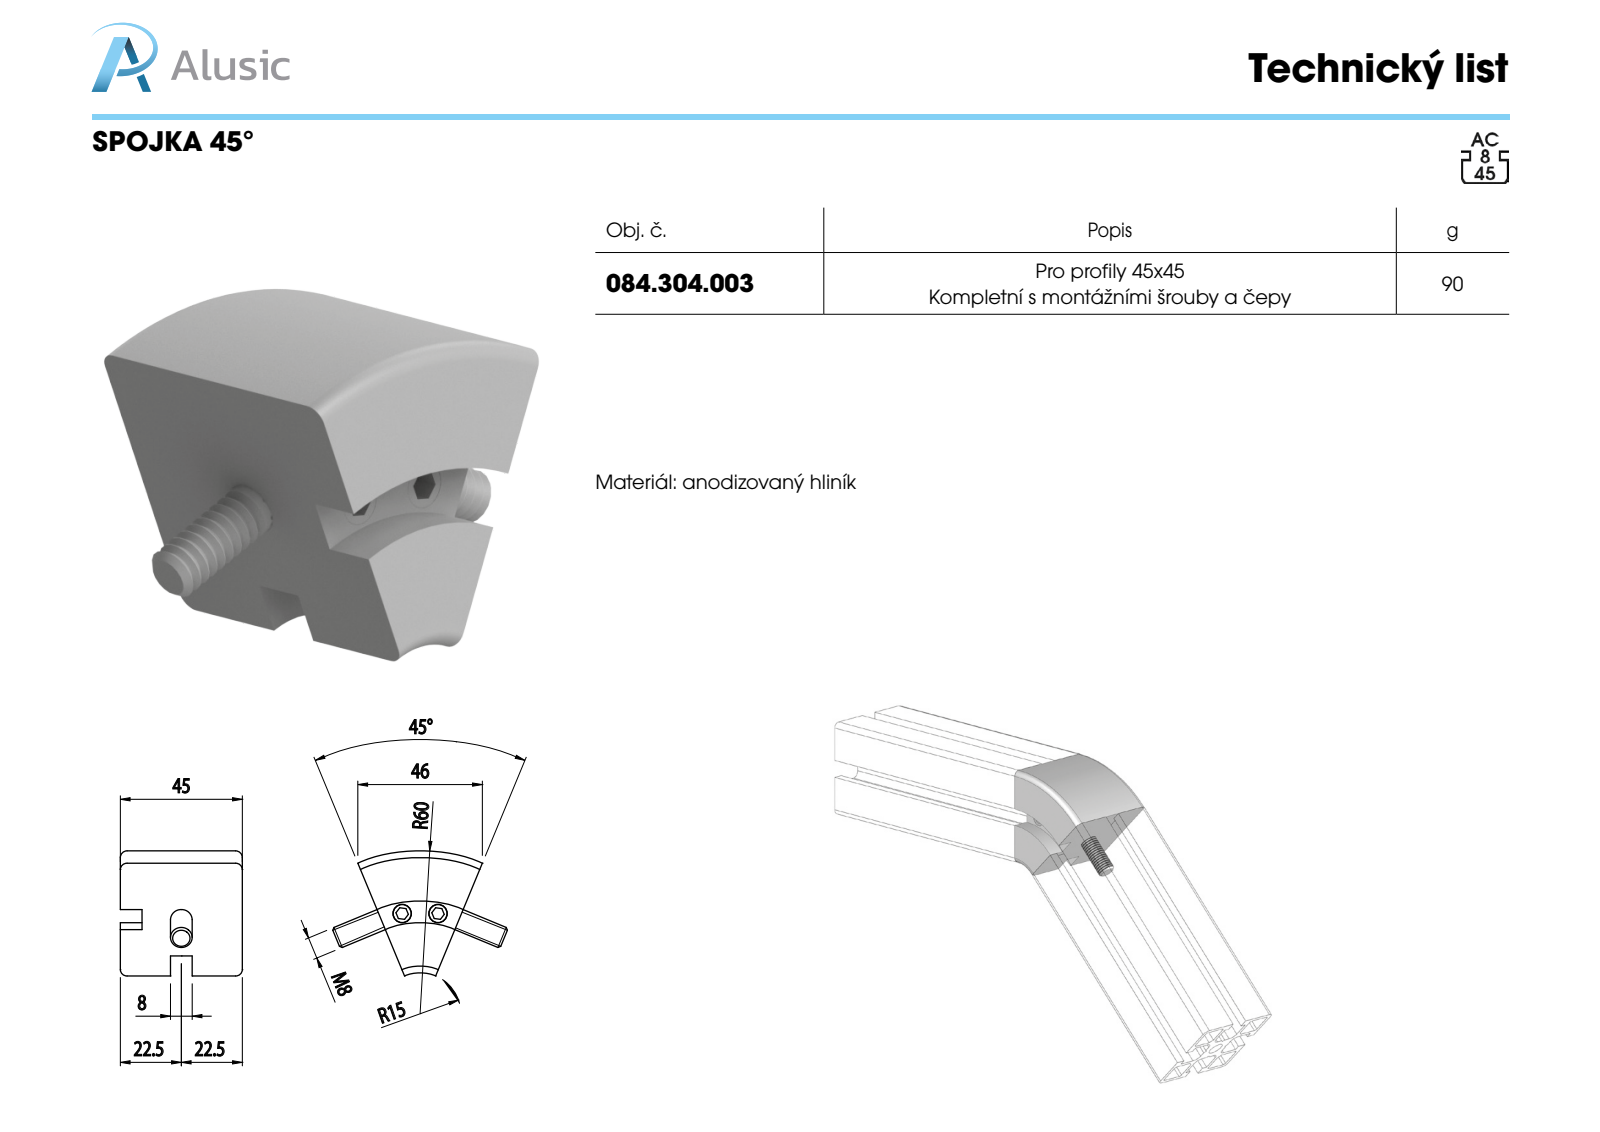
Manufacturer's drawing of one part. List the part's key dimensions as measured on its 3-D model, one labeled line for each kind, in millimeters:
Part name (STEP PRODUCT): 084.304.003
STEP written by: SolidWorks 2016 (CONFIG_CONTROL_DESIGN)
Units: millimetres
Bodies: 1 solid, 36 faces (12 planar, 16 cylindrical, 8 other)
Overall size (bounding box): 49.39 × 45 × 42.43
Volume: 52 566 mm³ · Surface area: 11 069 mm²
Round holes (diameter × count): ⌀6.8 ×2, ⌀8 ×2
Partial cylindrical surfaces — rounded edges, fillets, slot ends (radius × count): R15 ×1, R23 ×1, R33.5 ×1, R41.5 ×1, R60 ×1
Main face-to-face distances: 45, 8, 18.5, 37, 26.5, 10.5, 29, 22.5, 14.5, 4
Hole centre spacings: 13.23
